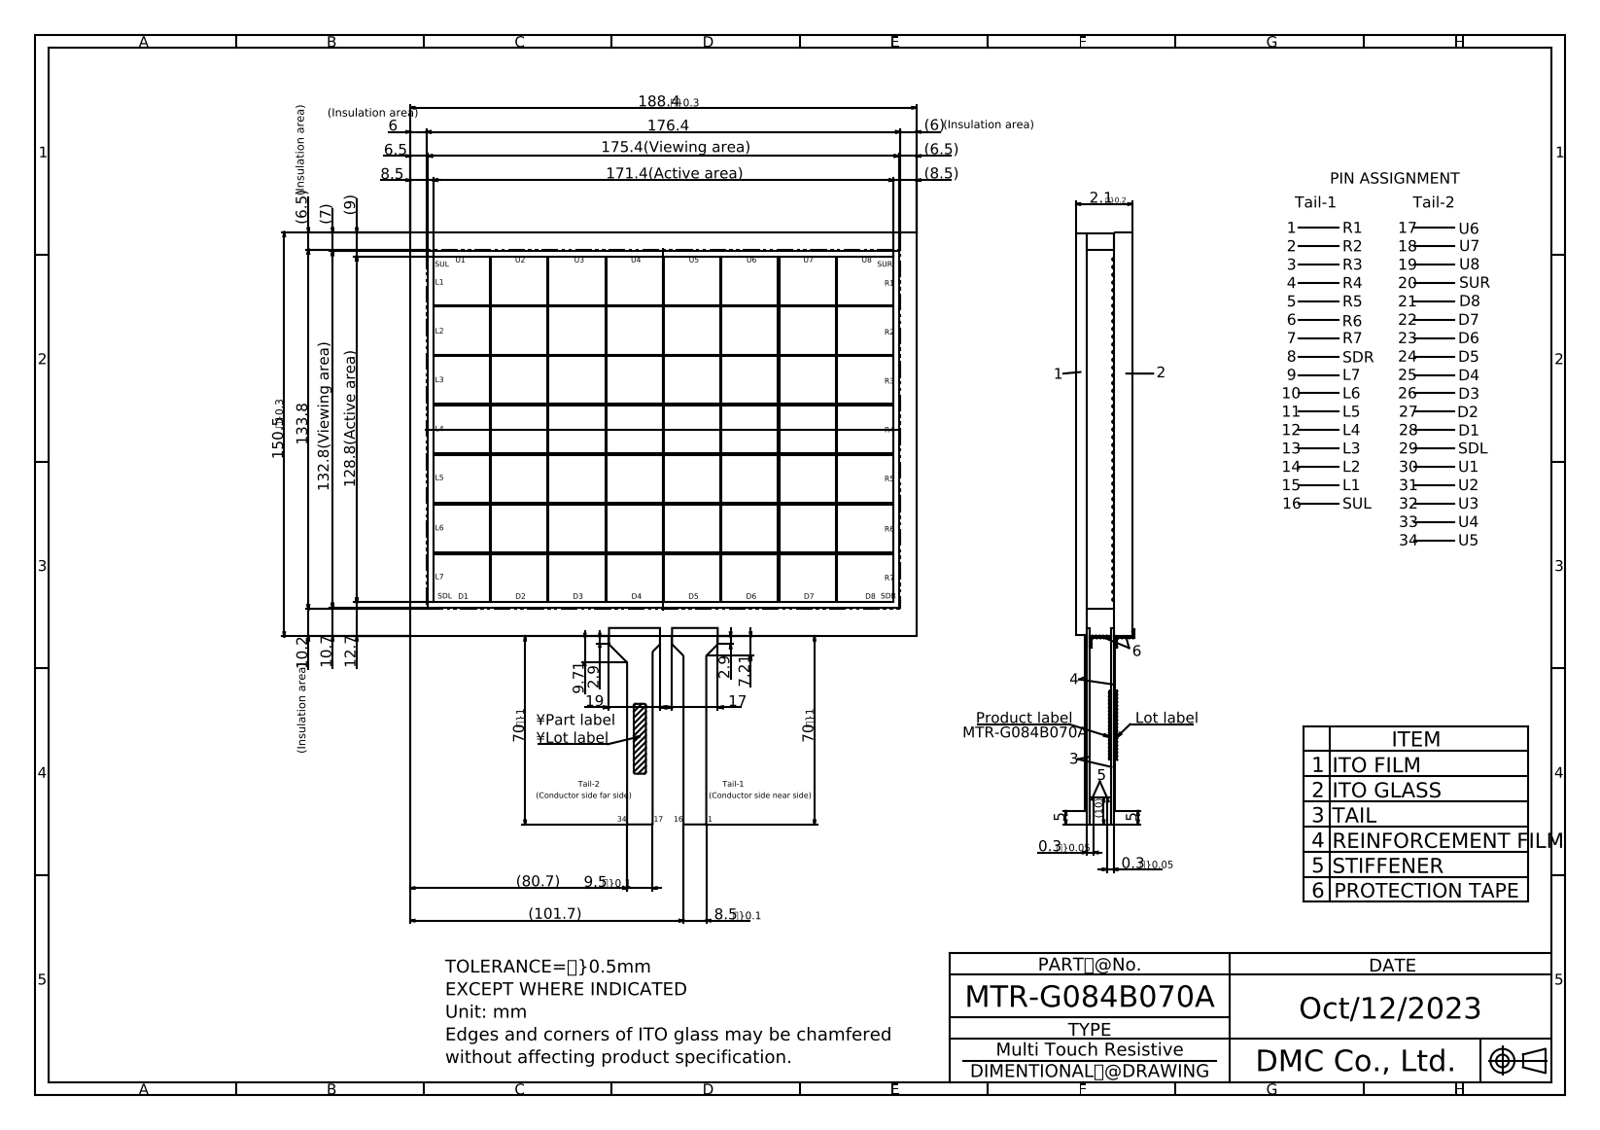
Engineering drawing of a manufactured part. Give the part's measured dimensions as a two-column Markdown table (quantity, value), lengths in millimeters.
| quantity | value |
| --- | --- |
| part name | MTR-G084B070A |
| STEP written by | Autodesk Inventor 2020 (CONFIG_CONTROL_DESIGN) |
| units | millimeters |
| bodies | 1 solid, 190 faces (178 planar, 12 cylindrical, 0 other) |
| overall size | 263.76 × 250.6 × 2.2 |
| volume | 59 602 mm³ |
| surface area | 61 017 mm² |
| partial cylindrical surfaces (radius × count) | 1 × 8, 0.2 × 4 |
| main face-to-face distances | 2.1, 2, 1.8, 1.9, 150.5, 188.4, 0.4, 2.2, 0.5, 0.7 |
